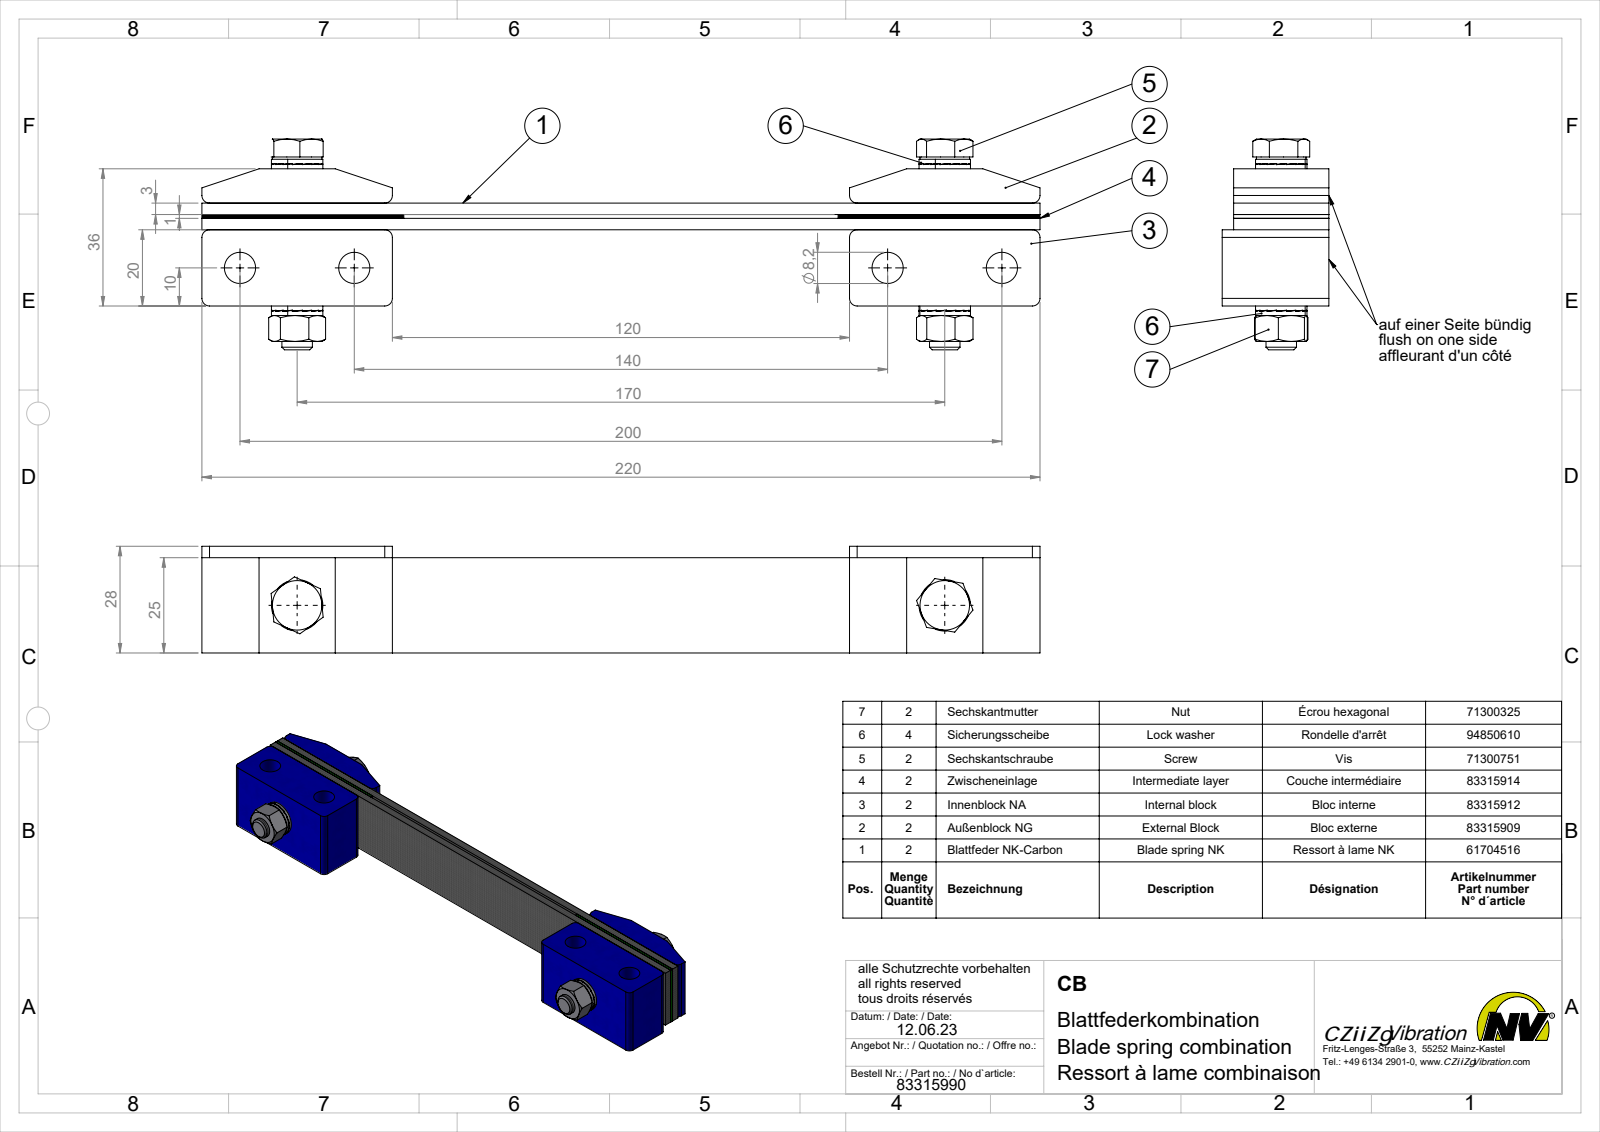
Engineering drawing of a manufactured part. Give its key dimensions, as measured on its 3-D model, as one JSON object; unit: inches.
{"part_name": "Blattfederkombination CB # 83315990", "step_written_by": "SolidWorks 2022 (AUTOMOTIVE_DESIGN)", "units": "inches", "bodies": {"solids": 16, "faces": 686, "planar": 554, "cylindrical": 80, "other": 52}, "overall_size": [8.661, 2.177, 1.102], "volume_in3": 6.664, "surface_area_in2": 90.95, "round_holes": [[0.323, 6], [0.268, 2], [0.315, 2], [0.335, 2], [0.343, 2]], "round_bosses_or_shafts": [[0.531, 2], [0.512, 2]], "partial_cylinders_radius": [[0.079, 12]], "face_to_face_distances": [0.118, 0.157, 0.039, 0.276, 1.063, 0.945, 0.906, 0.787, 0.984, 1.102], "hole_center_spacings": [6.693, 1.181, 5.512, 7.874]}
